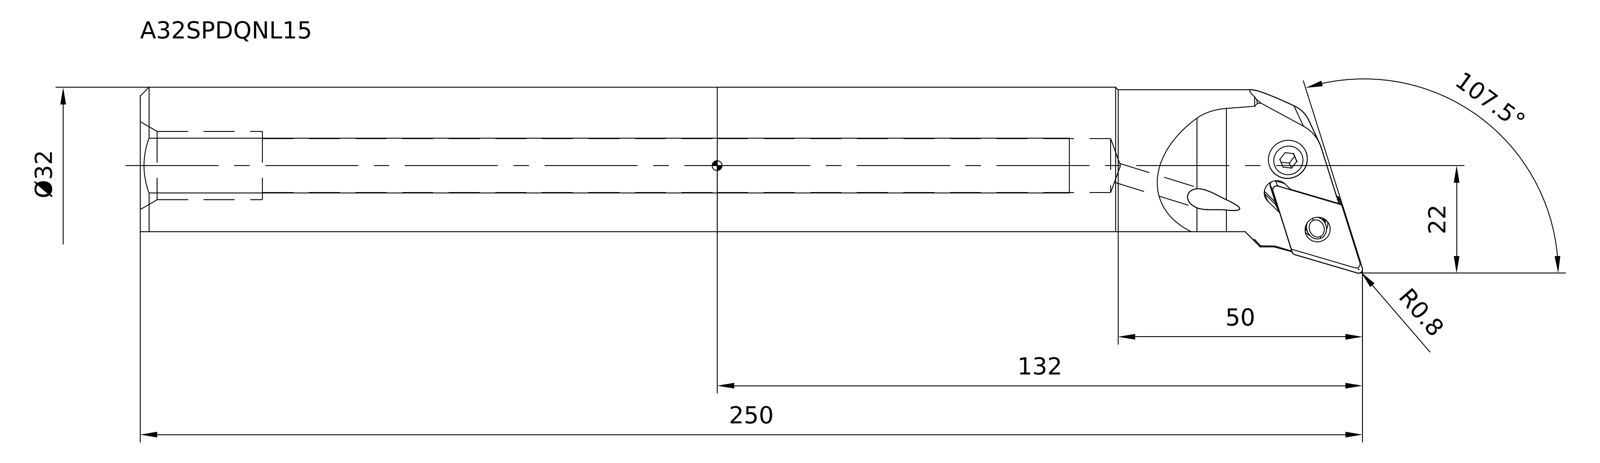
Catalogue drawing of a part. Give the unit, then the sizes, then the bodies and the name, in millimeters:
Units: millimetres
Overall size (bounding box): 249.5 × 36.94 × 33.5
Round holes (diameter × count): ⌀4 ×2, ⌀5 ×2, ⌀6.5 ×1, ⌀8.12 ×1, ⌀11 ×1, ⌀14 ×1
Round bosses / shafts (diameter × count): ⌀32 ×1, ⌀31 ×1, ⌀8 ×1, ⌀6.5 ×1, ⌀4.99 ×1, ⌀3.6 ×1
Partial cylindrical surfaces — rounded edges, fillets, slot ends (radius × count): R0.3 ×4, R2.6 ×4, R0.4 ×2, R0.5 ×2, R7 ×2, R0.8 ×1, R1.2 ×1, R2.2 ×1
Main face-to-face distances: 30, 7.43, 3.18, 4.25, 10, 4.95, 8, 5.2, 2.5, 32.5
Hole centre spacings: 4.71, 11.25, 15.96
Volume: 158 259 mm³ · Surface area: 36 426 mm²
Bodies: 7 solids, 203 faces (75 planar, 67 cylindrical, 61 other)
Part name (STEP PRODUCT): A32SPDQNL15_ASM
STEP written by: SIEMENS PLM Software NX 10.0 (AUTOMOTIVE_DESIGN)
